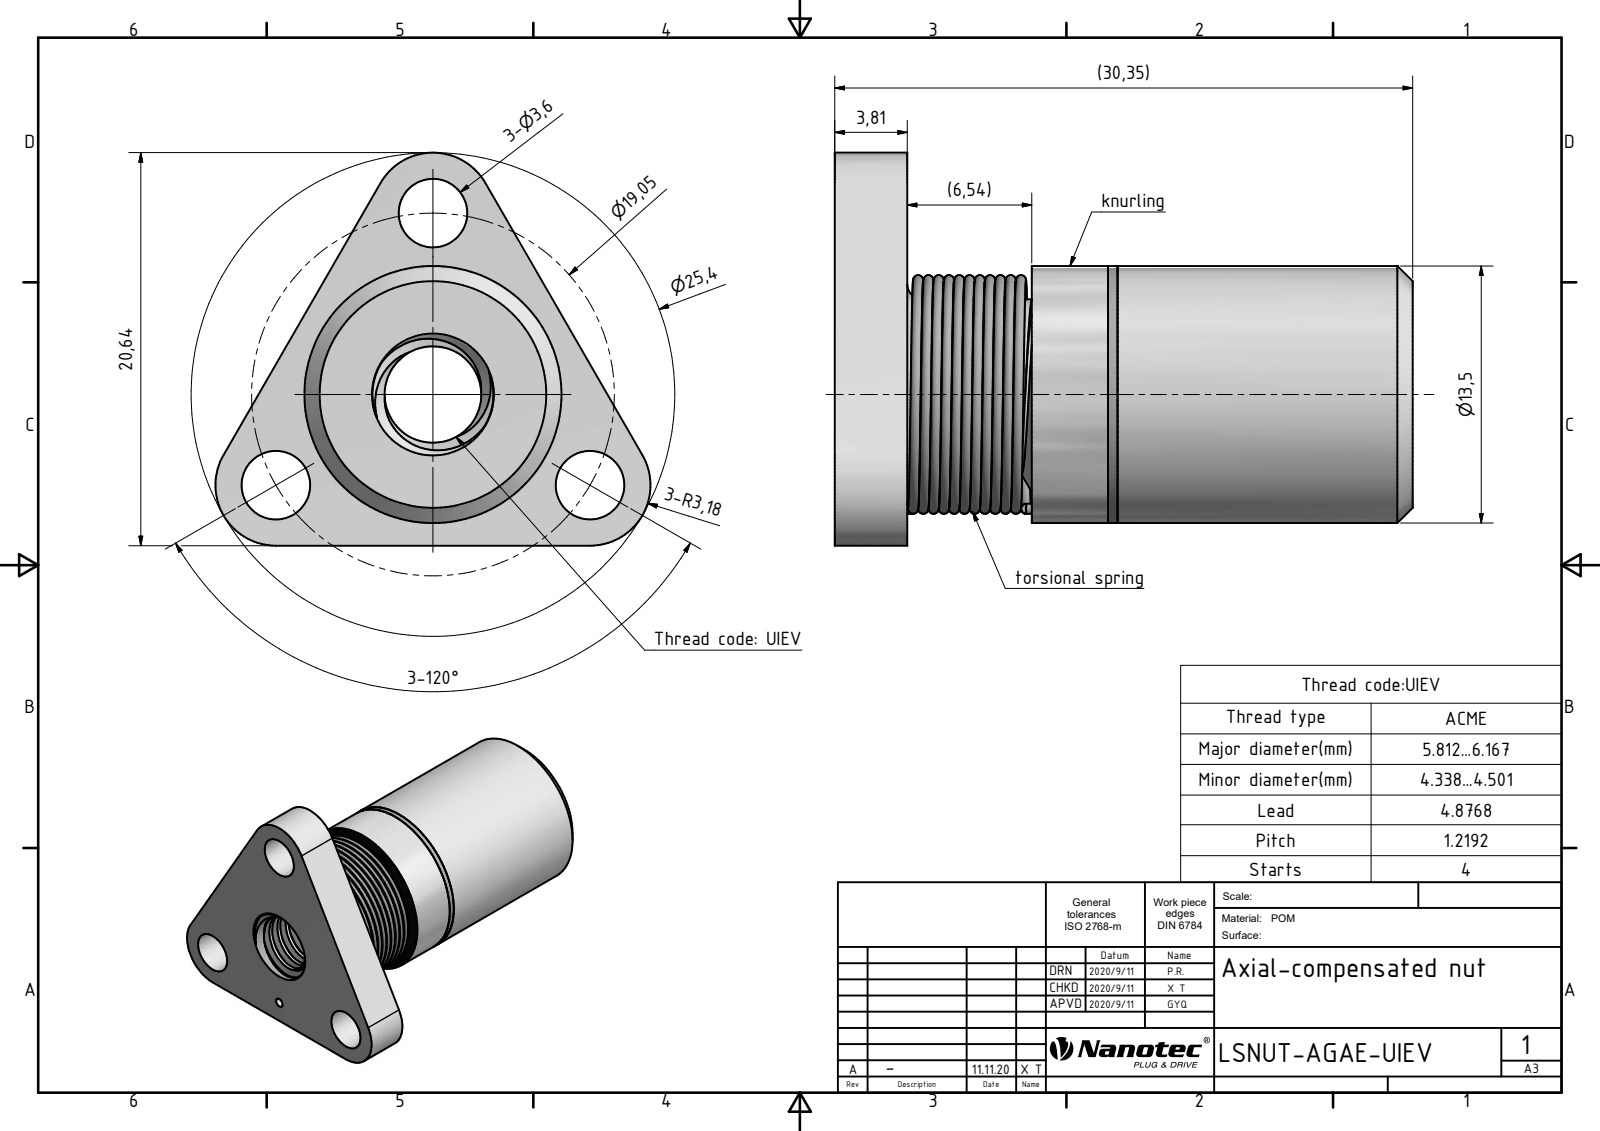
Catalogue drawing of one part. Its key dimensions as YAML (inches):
part_name: "20000655"
step_written_by: "Autodesk Inventor 2019 (AUTOMOTIVE_DESIGN)"
units: inches
bodies: {solids: 4, faces: 45, planar: 17, cylindrical: 17, other: 11}
overall_size: [1.175, 0.9, 0.813]
volume: 0.206
surface_area: 6.29
round_holes:
  - {diameter: 0.142, count: 3}
  - {diameter: 0.026, count: 1}
  - {diameter: 0.031, count: 1}
  - {diameter: 0.236, count: 1}
  - {diameter: 0.394, count: 1}
  - {diameter: 0.433, count: 1}
round_bosses_or_shafts:
  - {diameter: 0.531, count: 1}
  - {diameter: 0.021, count: 1}
partial_cylinders:
  - {radius: 0.125, count: 3}
face_to_face_distances: [0.15, 0.565, 0.415, 1.175, 1.025, 0.61, 0.407, 0.257, 0.157, 0.768]
hole_center_spacings: [0.65, 0.328, 0.375, 0.236, 0.375, 0.611]
